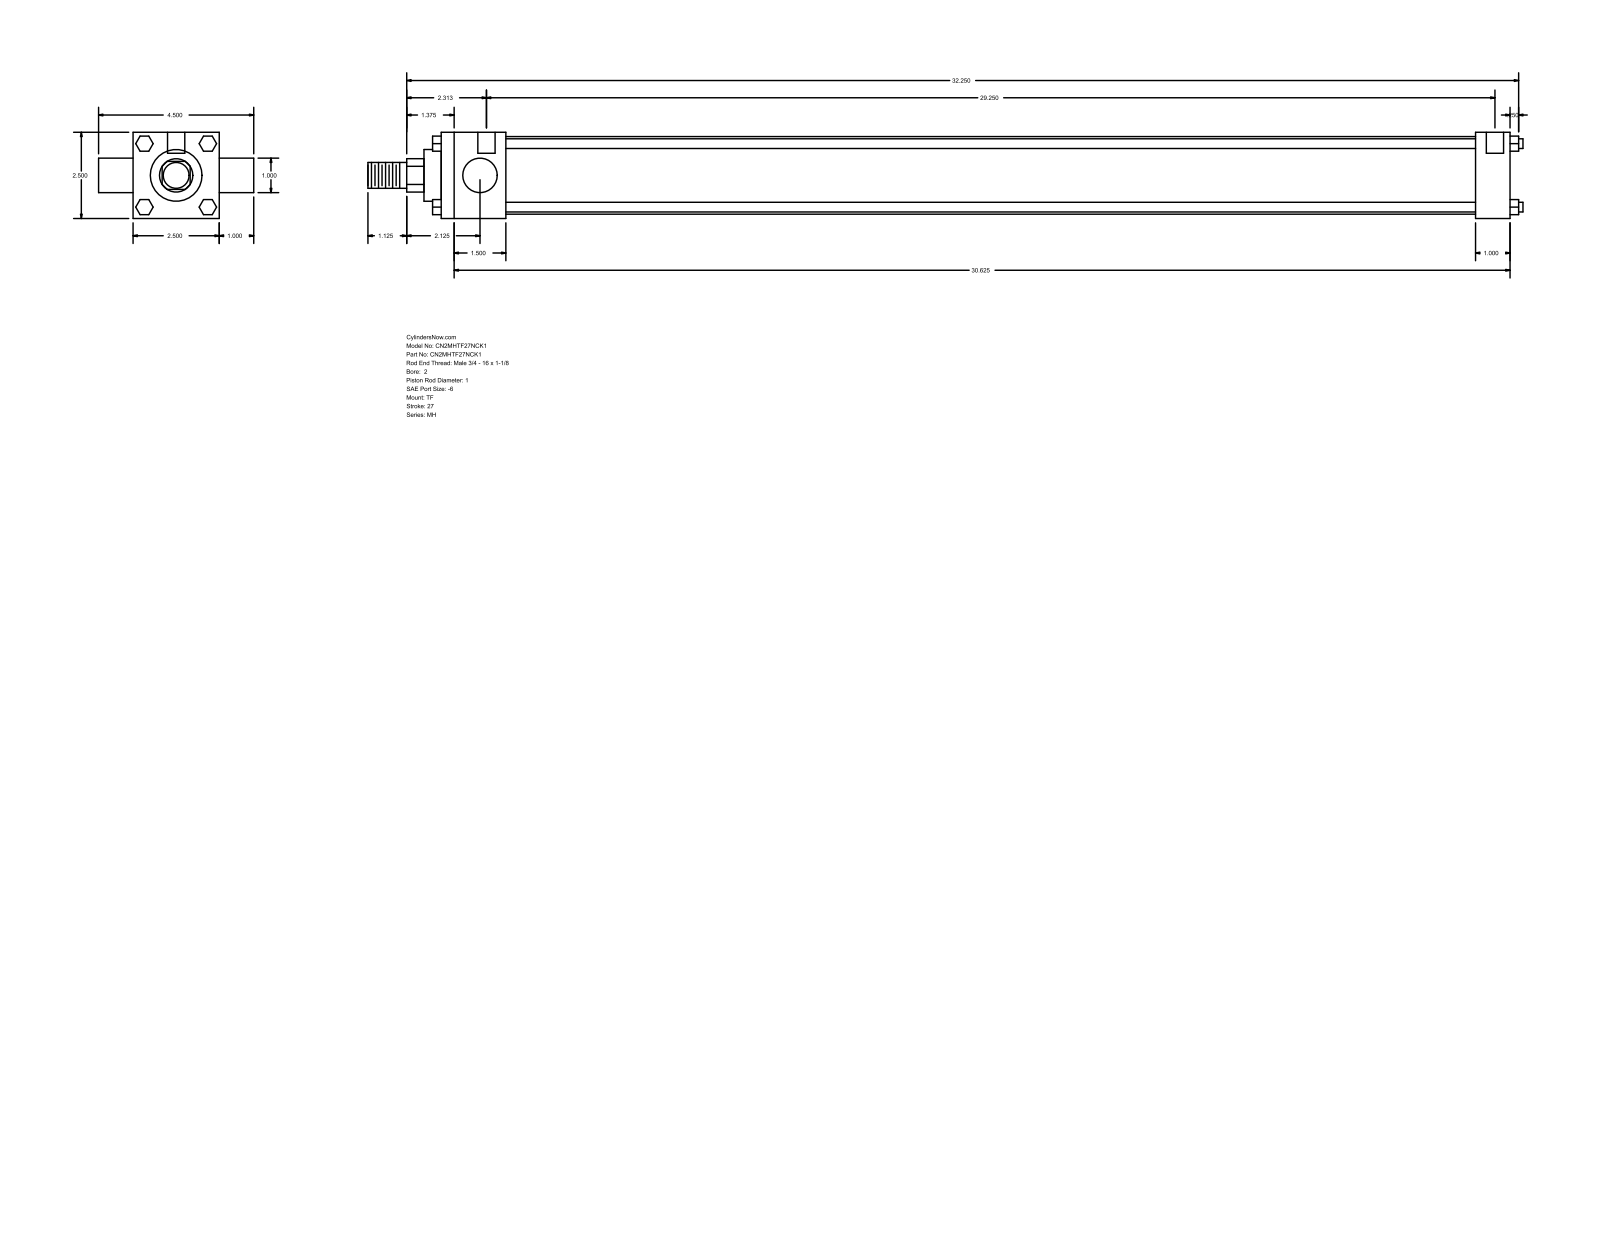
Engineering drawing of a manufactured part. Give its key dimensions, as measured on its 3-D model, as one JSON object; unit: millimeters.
{"part_name": "MH_TF__0200_1", "step_written_by": "GSSL Pune (CONFIG_CONTROL_DESIGN)", "units": "millimeters", "bodies": {"solids": 0, "faces": 120, "planar": 92, "cylindrical": 28, "other": 0}, "overall_size": [850.9, 114.3, 63.5], "round_holes": [[5.56, 3], [12.7, 2]], "round_bosses_or_shafts": [[7.14, 4], [25.4, 2], [57.15, 1], [38.1, 1], [19.05, 1]], "partial_cylinders_radius": [[12.29, 1]], "face_to_face_distances": [63.5, 787.4, 25.4, 47.63, 762, 714.37, 739.77, 88.9, 800.1, 6.35], "hole_center_spacings": [3.17, 4.76, 742.95, 746.12, 747.71, 750.88]}
